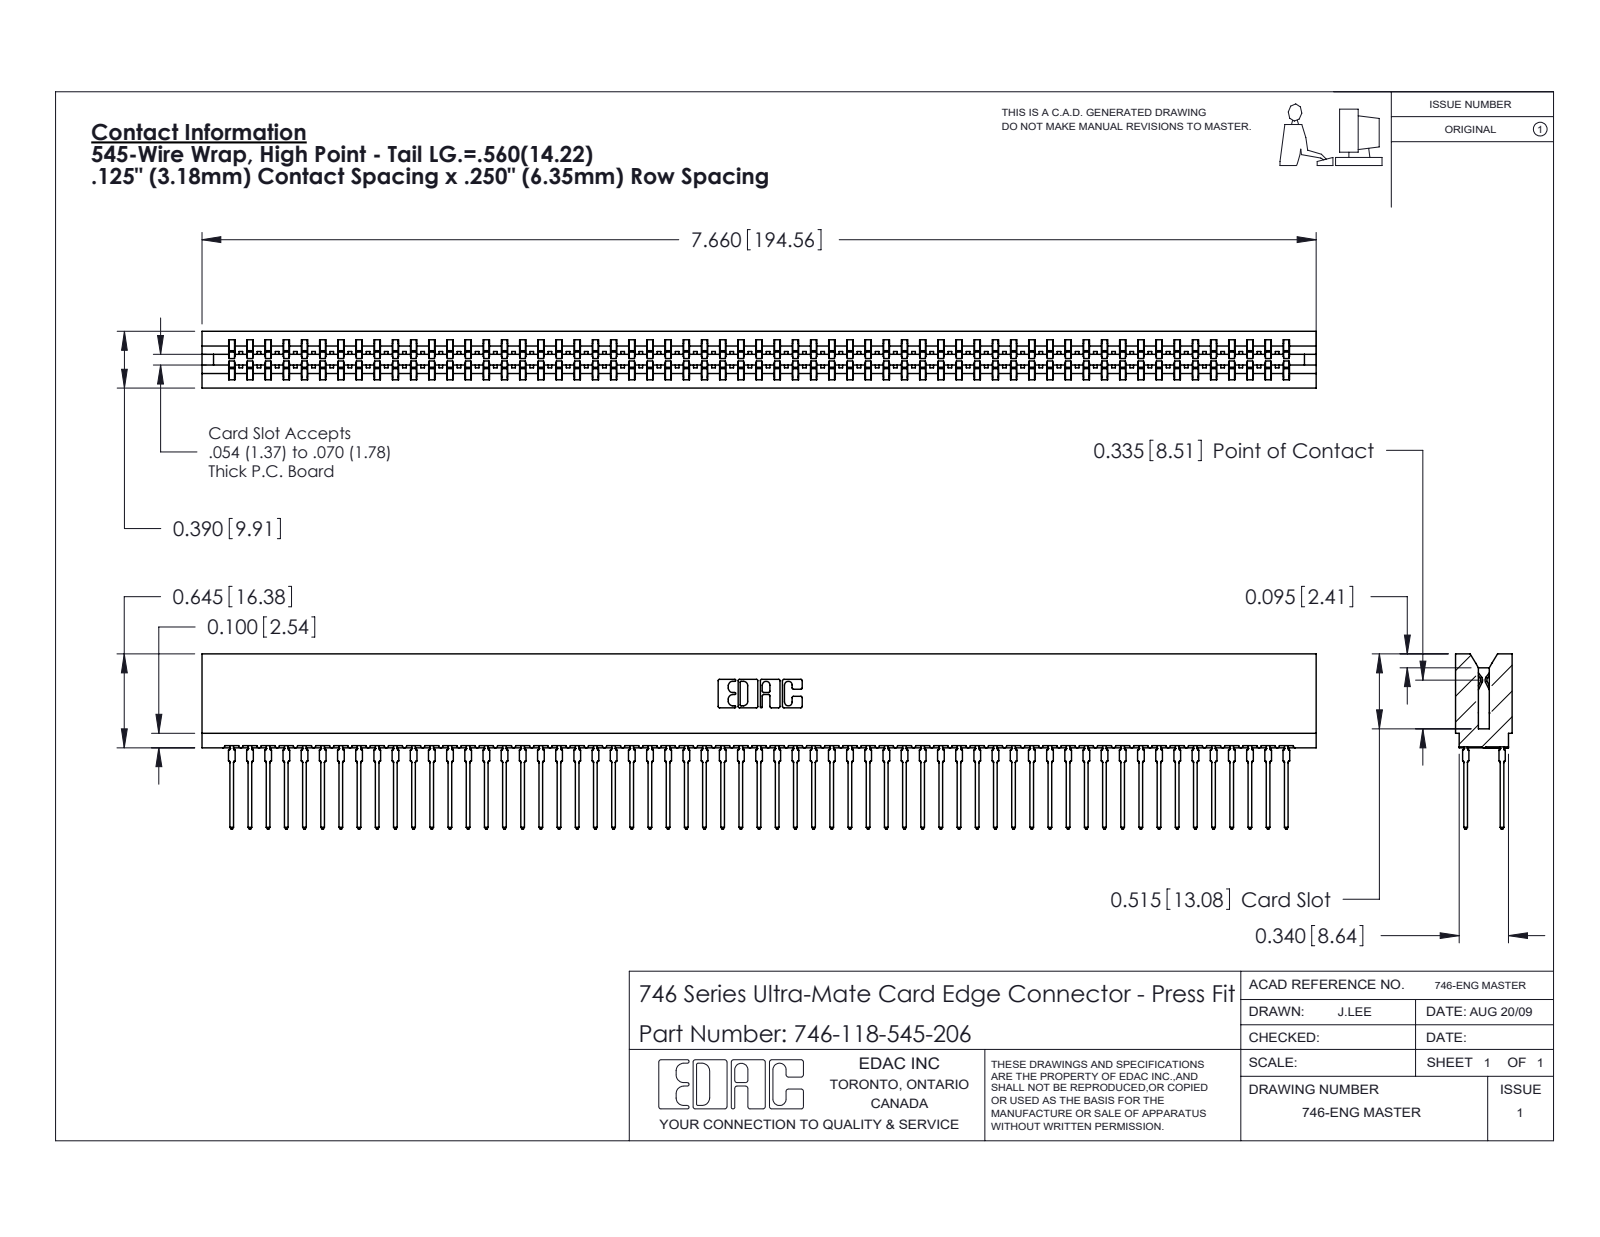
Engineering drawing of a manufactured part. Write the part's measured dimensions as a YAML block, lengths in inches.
part_name: "746-292-001_545; 746 Part_.515 Slot Depth - 06; 746-118-545-206"
step_written_by: "SolidWorks 2020 (CONFIG_CONTROL_DESIGN)"
units: inches
bodies: {solids: 119, faces: 10659, planar: 5484, cylindrical: 2107, other: 3068}
overall_size: [7.66, 1.204, 0.39]
volume: 1.289
surface_area: 56.07
partial_cylinders:
  - {radius: 0.021, count: 236}
  - {radius: 0.015, count: 60}
  - {radius: 0.01, count: 22}
  - {radius: 0.005, count: 8}
  - {radius: 0.011, count: 8}
  - {radius: 0.007, count: 6}
  - {radius: 0.031, count: 6}
  - {radius: 0.026, count: 3}
face_to_face_distances: [0.057, 0.333, 0.25, 0.39, 0.025, 0.307, 0.275, 0.083, 0.174, 0.158]
